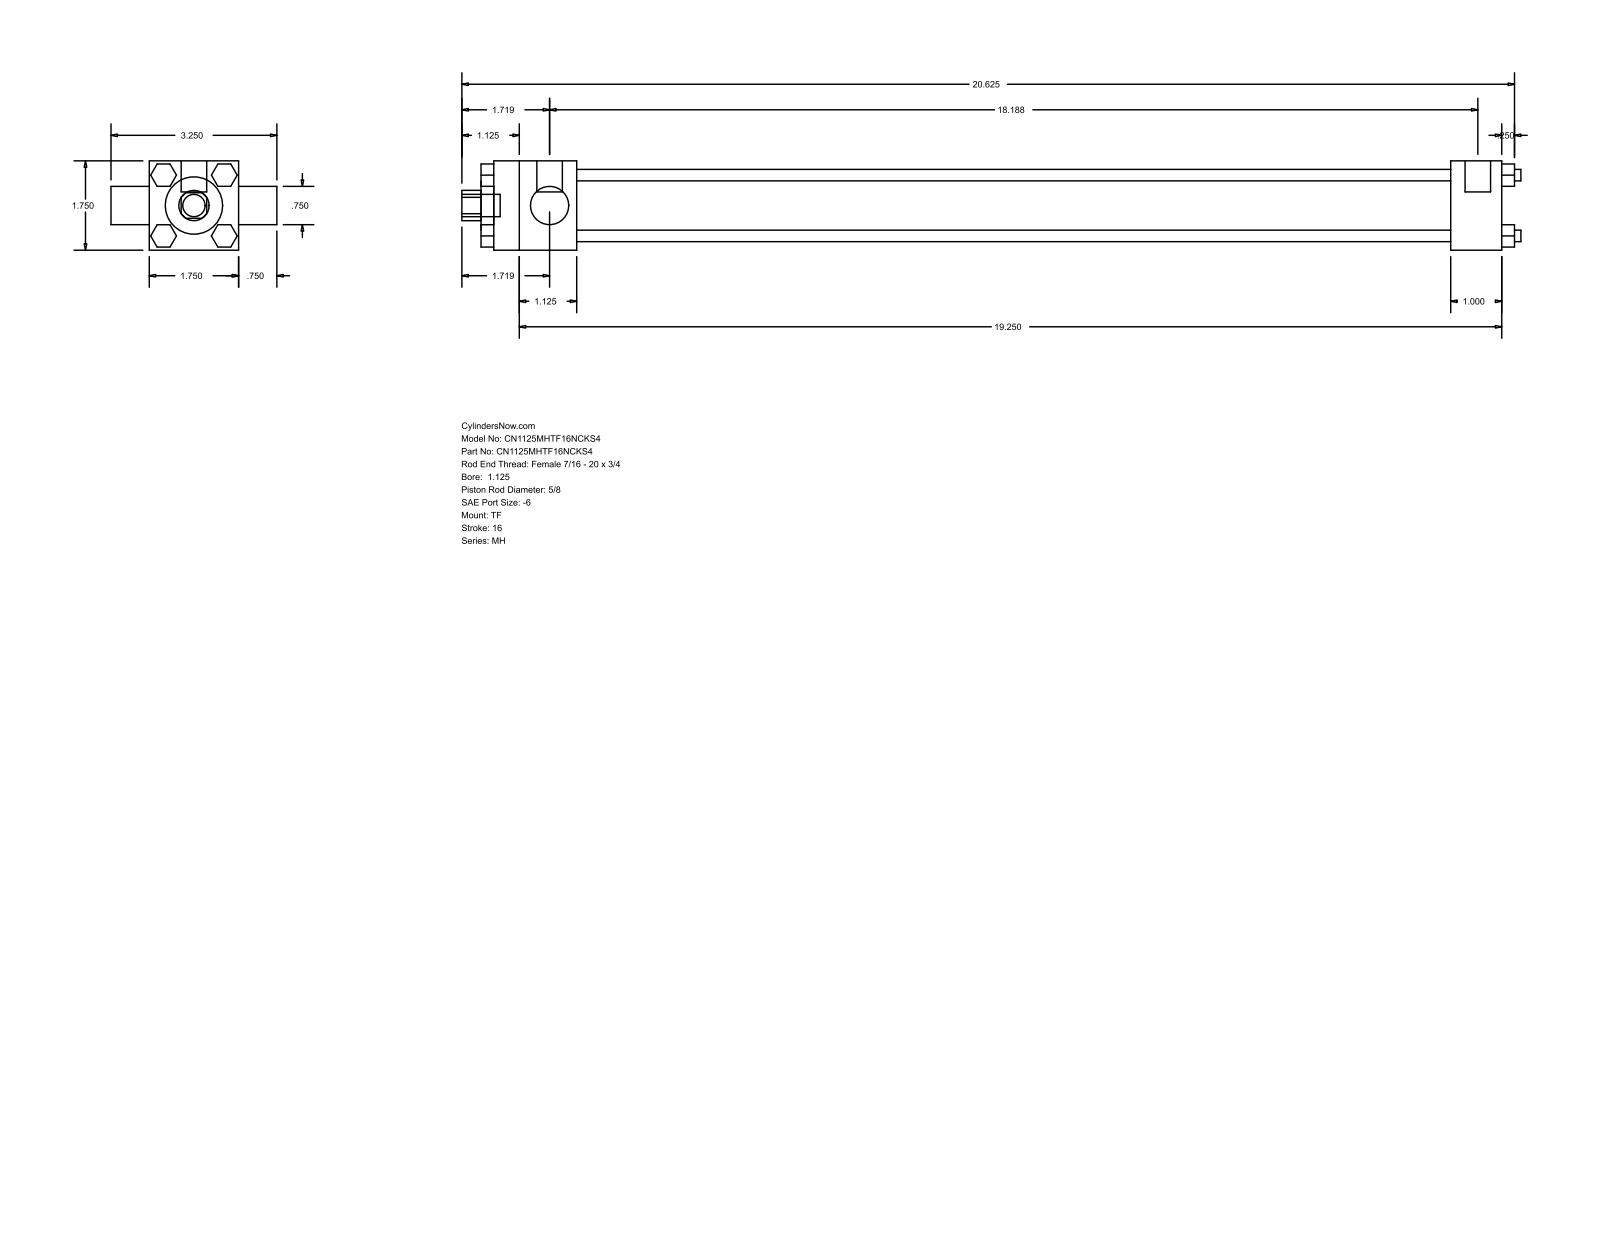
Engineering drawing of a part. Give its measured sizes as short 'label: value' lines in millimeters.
name: MH_TF__0112_0.625
written by: GSSL Pune (CONFIG_CONTROL_DESIGN)
unit: mm
bodies: 0 solids, 120 faces (92 planar, 28 cylindrical, 0 other)
size: 527.05 × 82.55 × 44.45
holes: 1× ⌀15.88, 1× ⌀19.05, 1× ⌀28.57, 1× ⌀34.92
bosses: 4× ⌀5.71, 3× ⌀5.56, 2× ⌀12.7, 1× ⌀11.11
rounds: 1× R7.54
face distances: 44.46, 11.11, 434.97, 460.37, 25.4, 41.27, 476.24, 501.64, 47.62, 6.35
